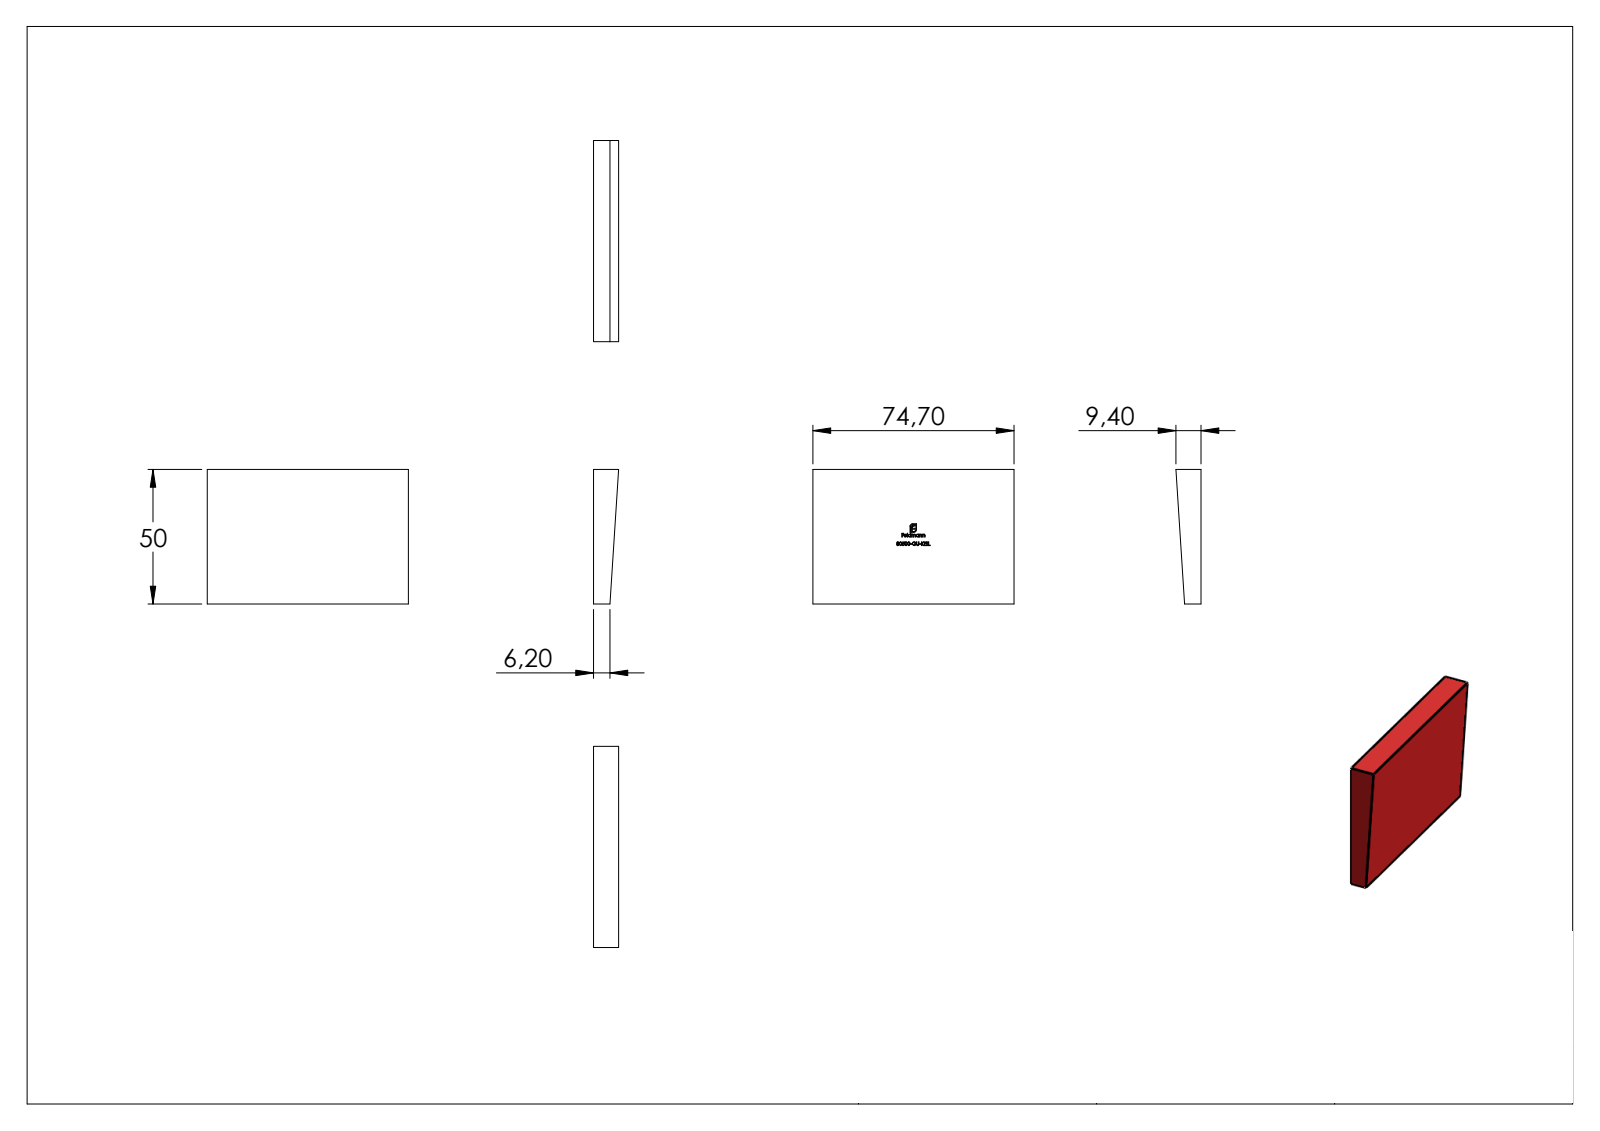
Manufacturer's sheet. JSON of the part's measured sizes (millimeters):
{"part_name": "80500-GU-KEIL", "step_written_by": "SolidWorks 2018 (CONFIG_CONTROL_DESIGN)", "units": "millimeters", "bodies": {"solids": 1, "faces": 305, "planar": 169, "cylindrical": 0, "other": 136}, "overall_size": [74.7, 50, 9.4], "volume_mm3": 29132, "surface_area_mm2": 9437, "face_to_face_distances": [50, 74.7, 0.34, 2.2, 1.95, 0.88, 6.11, 3.09, 25, 36.34]}
